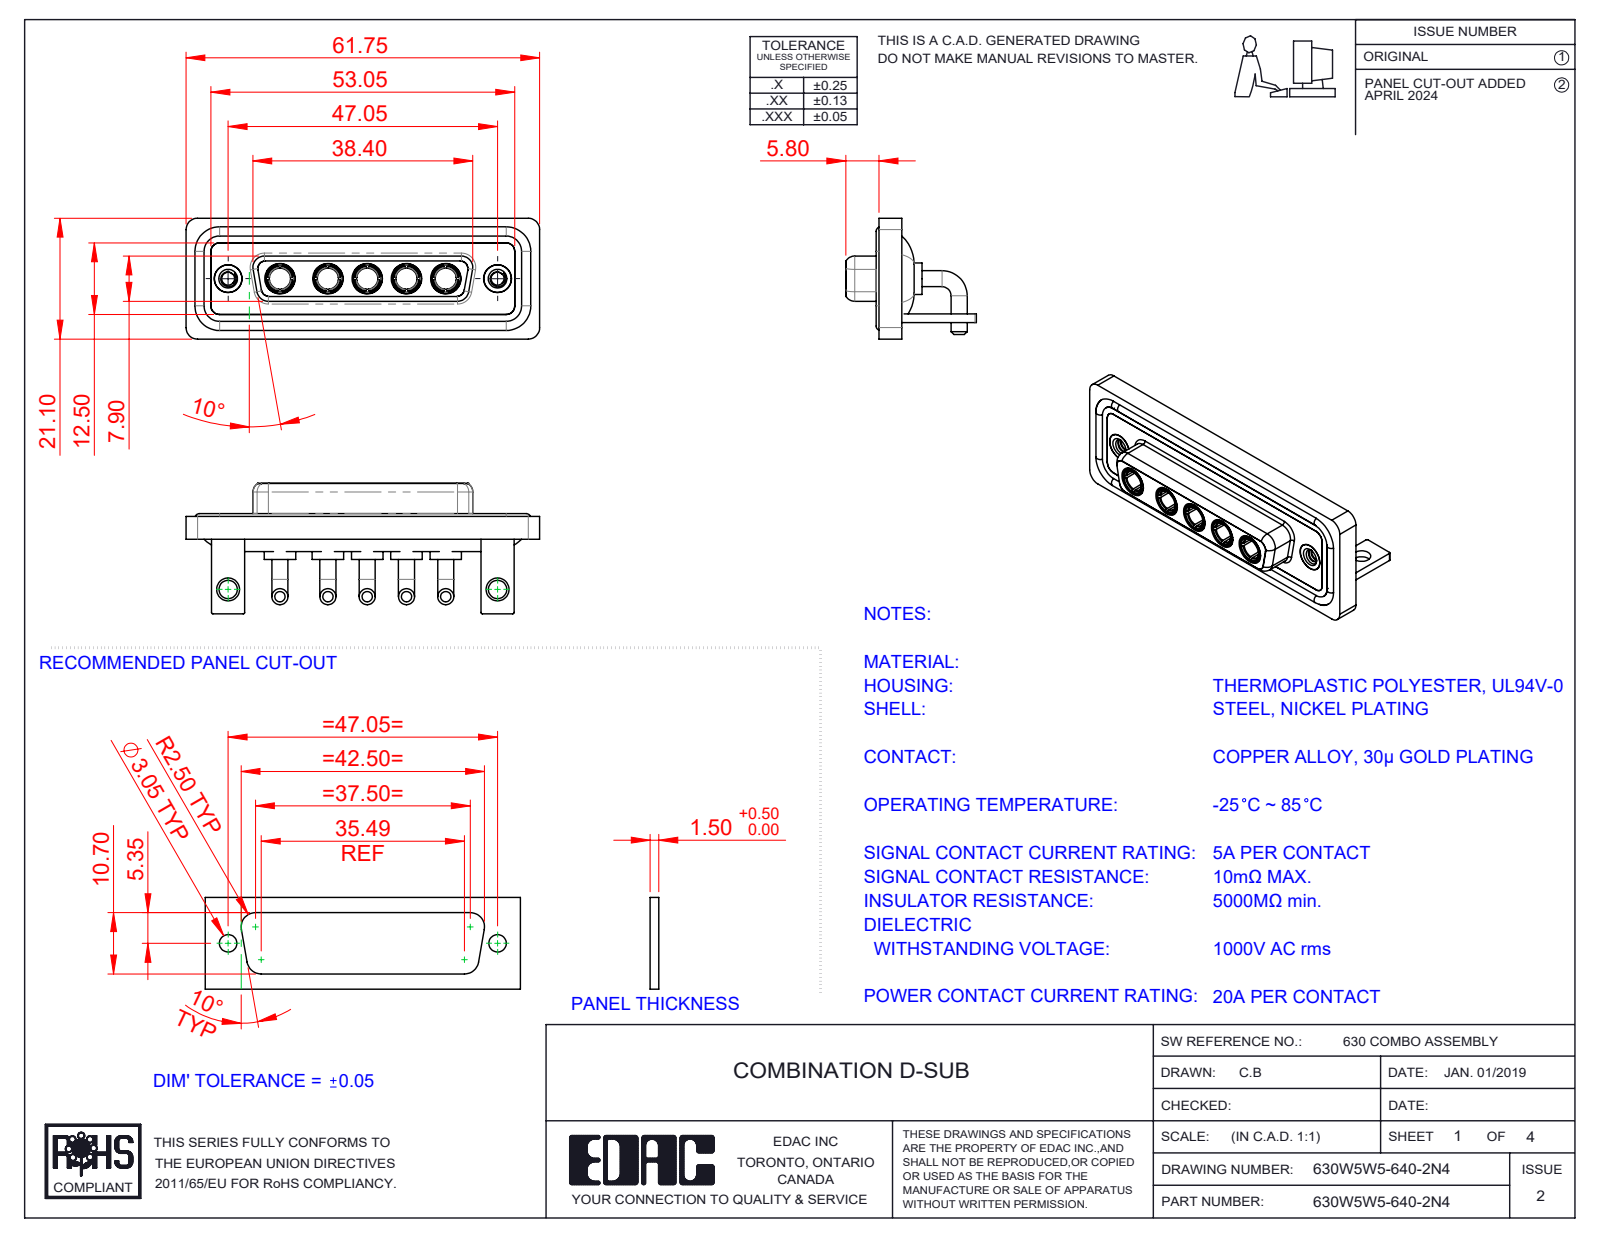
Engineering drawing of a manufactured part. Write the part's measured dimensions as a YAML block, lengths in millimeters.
part_name: "630Combo Shell Rear_25 Contacts; 630Combo Stabilizer Bracket_50 Contacts; 630Combo Shell Front_25 Contacts; 630Combo Waterproof Housing_25 Contacts (+4 more)"
step_written_by: "SolidWorks 2023 (CONFIG_CONTROL_DESIGN)"
units: millimeters
bodies: {solids: 19, faces: 824, planar: 270, cylindrical: 337, other: 217}
overall_size: [61.75, 22.8, 21.1]
volume: 8801
surface_area: 14548
round_holes:
  - {diameter: 4.85, count: 7}
  - {diameter: 3.7, count: 5}
  - {diameter: 5.3, count: 5}
  - {diameter: 2.26, count: 2}
  - {diameter: 3.2, count: 2}
  - {diameter: 4, count: 2}
  - {diameter: 4.05, count: 2}
  - {diameter: 5, count: 2}
round_bosses_or_shafts:
  - {diameter: 2.8, count: 10}
  - {diameter: 5.5, count: 5}
  - {diameter: 5.2, count: 5}
  - {diameter: 4.96, count: 5}
  - {diameter: 4.75, count: 5}
  - {diameter: 3.75, count: 5}
  - {diameter: 1.6, count: 4}
  - {diameter: 4.95, count: 2}
partial_cylinders:
  - {radius: 2, count: 19}
  - {radius: 1.5, count: 18}
  - {radius: 0.25, count: 16}
  - {radius: 1.35, count: 8}
  - {radius: 1.6, count: 8}
  - {radius: 0.5, count: 5}
  - {radius: 2.1, count: 5}
  - {radius: 0.6, count: 4}
face_to_face_distances: [0.4, 1.8, 2.9, 3.7, 1.5, 4.1, 1.1, 1.4, 1.6, 2.5]
hole_center_spacings: [6.86, 9.04, 38.01, 47.05, 6.87, 8.38, 13.72, 13.73]
